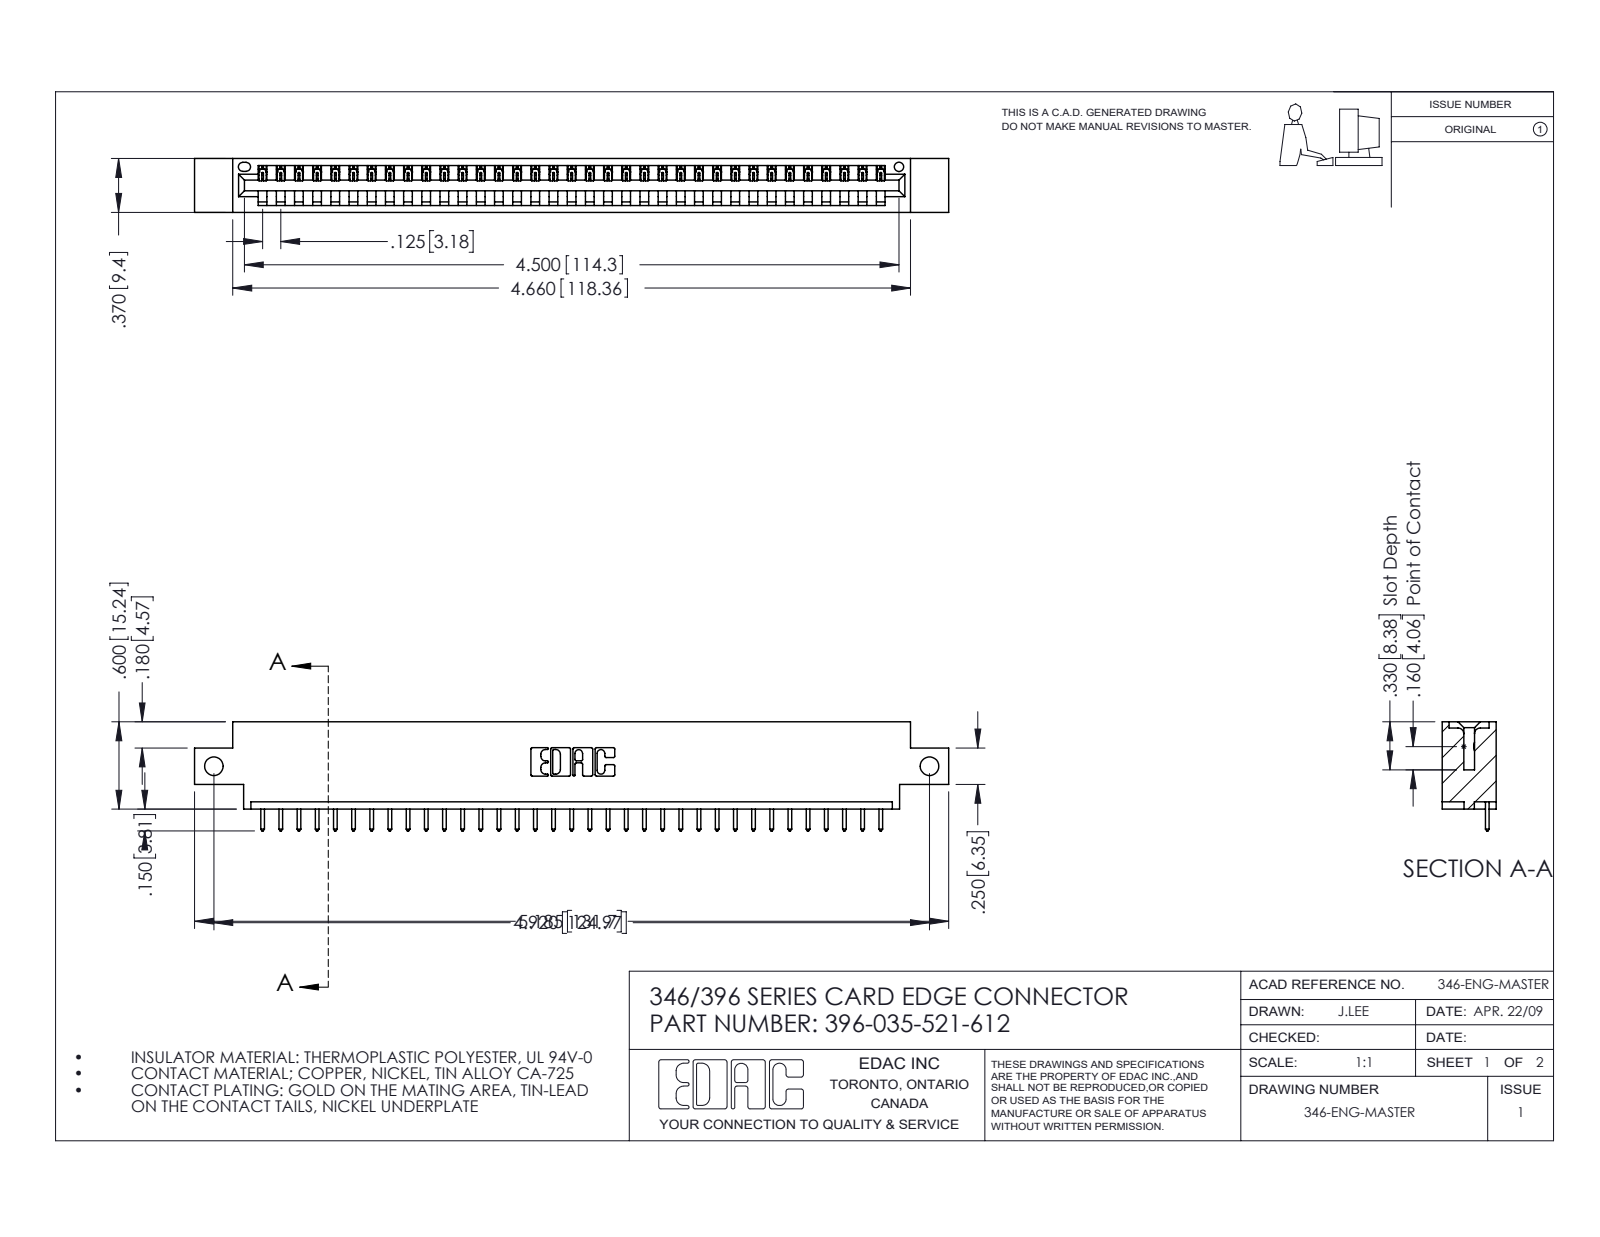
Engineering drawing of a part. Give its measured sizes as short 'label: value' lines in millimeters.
name: 396-035-521-612; 346 Part_0.170 Offset - Side Mount; 345-292-001_345-293-121
written by: SolidWorks 2016 (CONFIG_CONTROL_DESIGN)
unit: mm
bodies: 36 solids, 2156 faces (1480 planar, 676 cylindrical, 0 other)
size: 131.7 × 19.1 × 9.4
volume: 12 200 mm³; area: 14 810 mm²
holes: 2× ⌀3.3, 1× ⌀1.6
rounds: 70× R0.2, 70× R0.3, 22× R0.3, 6× R0.2, 6× R0.8, 3× R0.7, 2× R0.8, 2× R1
face distances: 1.2, 8.2, 9.4, 6.4, 1.8, 7.6, 0.6, 3.8, 5.6, 2.5
hole spacings: 125
